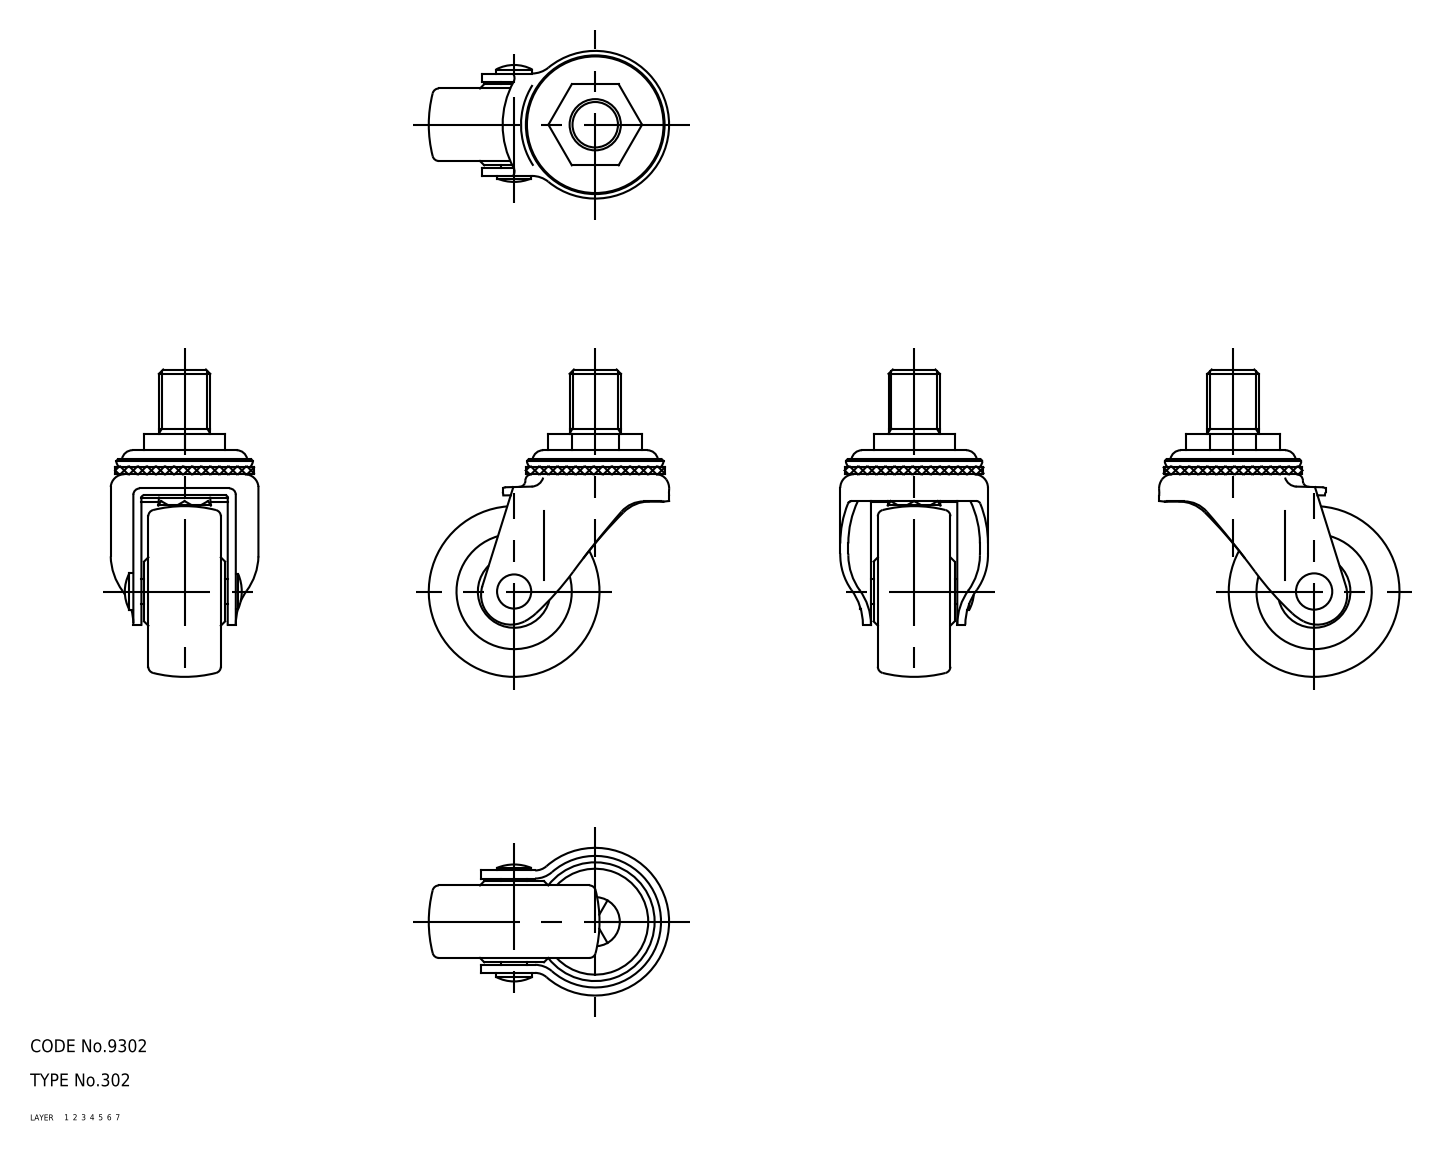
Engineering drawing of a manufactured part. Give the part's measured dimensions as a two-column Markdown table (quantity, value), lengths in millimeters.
| quantity | value |
| --- | --- |
| part name | wheel; main shaft; axle; No_302_23120_36 |
| STEP written by | CADfix (AUTOMOTIVE_DESIGN) |
| units | millimeters |
| bodies | 4 solids, 158 faces (0 planar, 0 cylindrical, 158 other) |
| overall size | 72 × 56.3 × 34.6 |
| volume | 34 788 mm³ |
| surface area | 14 303 mm² |
